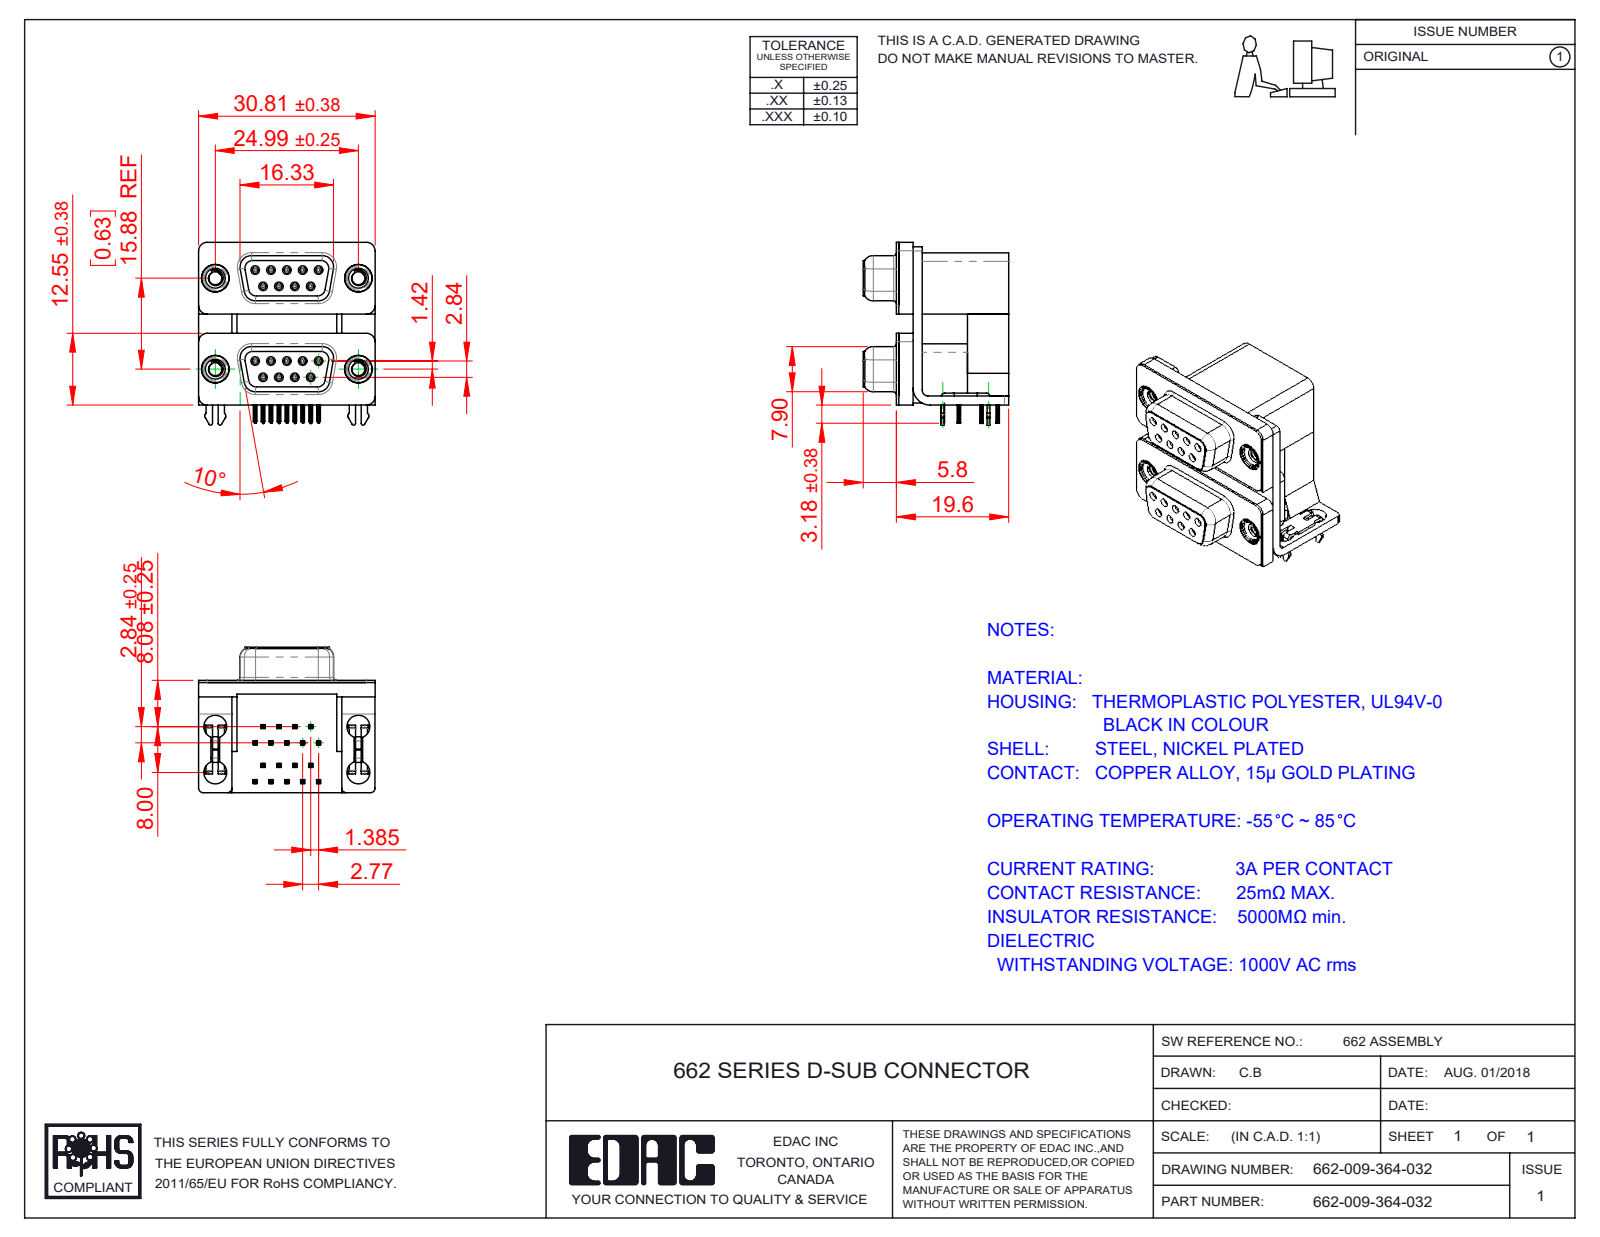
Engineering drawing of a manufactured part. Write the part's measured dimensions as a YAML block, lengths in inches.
part_name: "662 Contact Top Lower; 662 Threaded Rivet_4-40; 662 Housing Upper_09 Contacts L; 662 Contact Bottom Upper_L (+8 more)"
step_written_by: "SolidWorks 2020 (CONFIG_CONTROL_DESIGN)"
units: inches
bodies: {solids: 31, faces: 3262, planar: 1476, cylindrical: 846, other: 940}
overall_size: [1.257, 1.213, 1]
volume: 0.663
surface_area: 20.22
round_holes:
  - {diameter: 0.031, count: 18}
  - {diameter: 0.035, count: 18}
  - {diameter: 0.157, count: 8}
  - {diameter: 0.089, count: 4}
  - {diameter: 0.138, count: 4}
  - {diameter: 0.189, count: 4}
  - {diameter: 0.197, count: 4}
round_bosses_or_shafts:
  - {diameter: 0.047, count: 18}
  - {diameter: 0.193, count: 4}
  - {diameter: 0.187, count: 4}
  - {diameter: 0.154, count: 4}
partial_cylinders:
  - {radius: 0.004, count: 146}
  - {radius: 0.006, count: 72}
  - {radius: 0.014, count: 36}
  - {radius: 0.013, count: 18}
  - {radius: 0.053, count: 18}
  - {radius: 0.02, count: 12}
  - {radius: 0.059, count: 12}
  - {radius: 0.01, count: 10}
face_to_face_distances: [0.098, 0.016, 0.657, 0.756, 0.114, 0.772, 0.625, 0.283, 0.374, 0.472]
hole_center_spacings: [0.124, 0.109, 0.635, 0.625, 0.218, 0.662, 0.516, 0.739]
